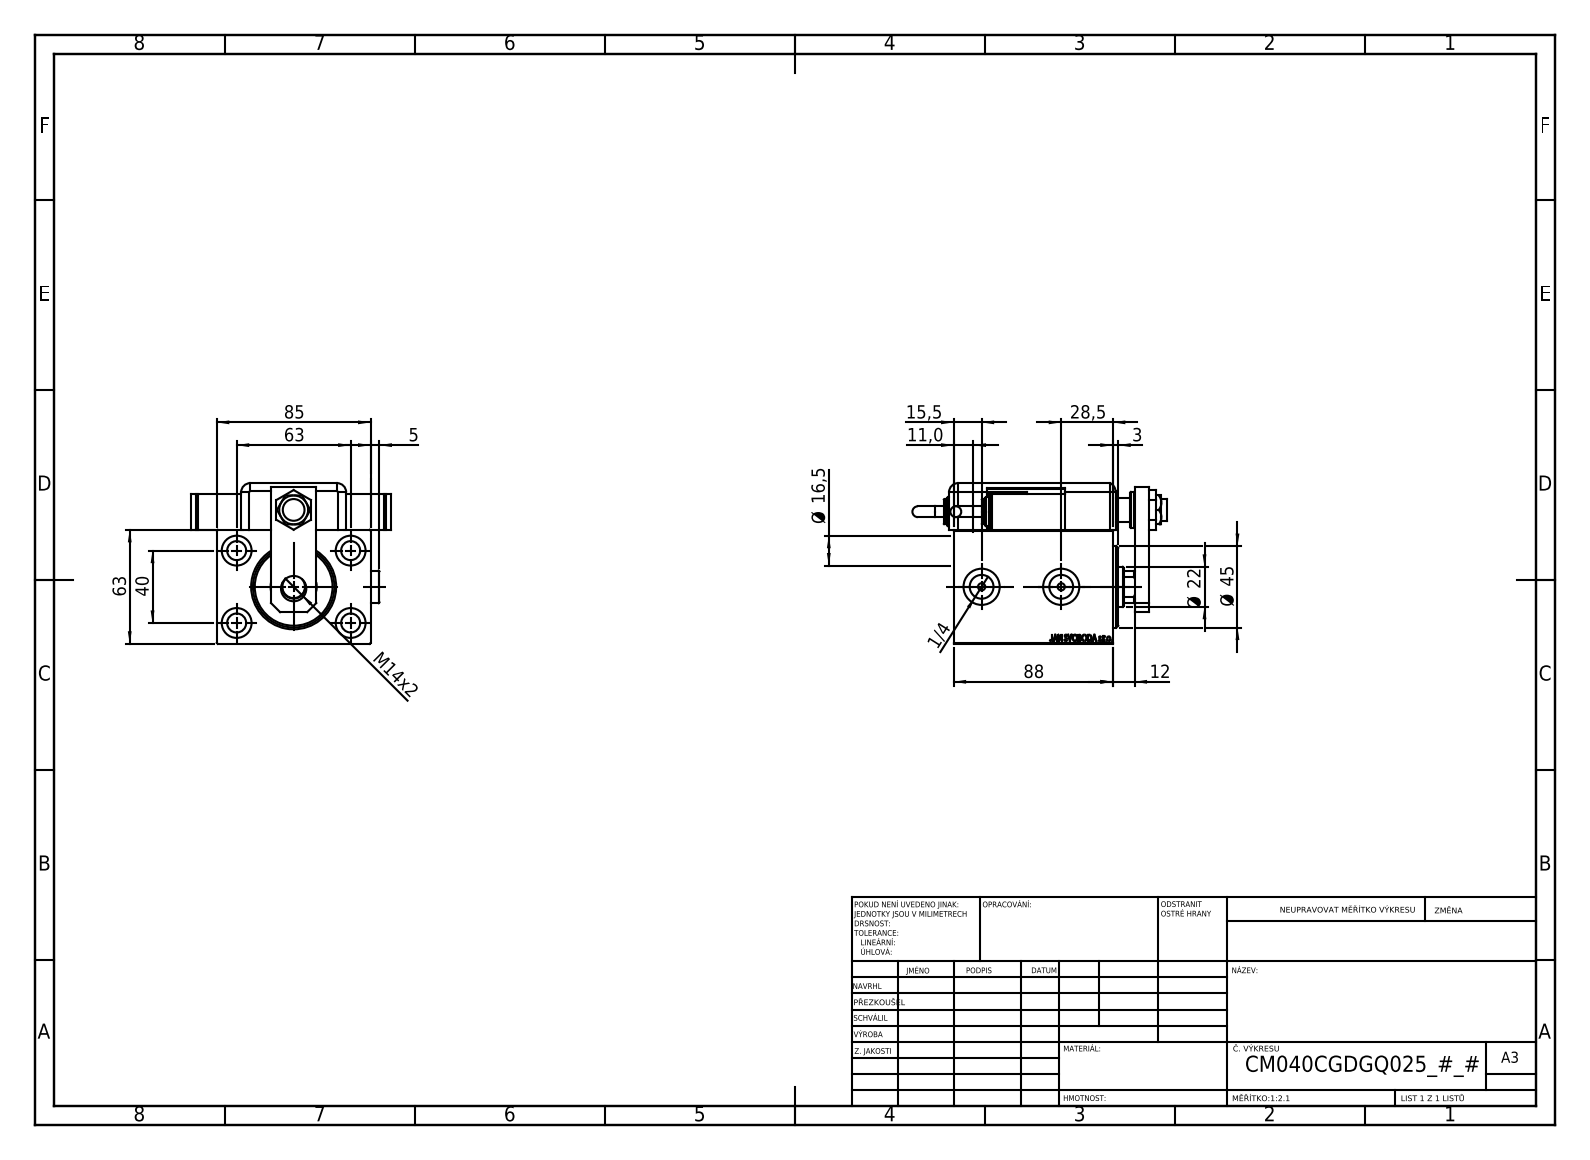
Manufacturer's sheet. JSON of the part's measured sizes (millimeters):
{"part_name": "TYC; V450CM_VC_B; KRYT; NUT_D19 (+7 more)", "step_written_by": "SolidWorks 2019 (CONFIG_CONTROL_DESIGN)", "units": "millimeters", "bodies": {"solids": 15, "faces": 1300, "planar": 648, "cylindrical": 131, "other": 521}, "overall_size": [140.46, 111, 88.8], "volume_mm3": 540819, "surface_area_mm2": 130727, "round_holes": [[4, 4], [10.5, 4], [16.5, 4], [8, 2], [13.16, 2], [14, 2], [20, 2], [12, 1], [12.5, 1], [13, 1], [22, 1], [25.5, 1]], "round_bosses_or_shafts": [[20, 3], [18, 2], [16, 2], [14, 2], [6, 2]], "partial_cylinders_radius": [[5, 9], [10, 1], [10.5, 1]], "face_to_face_distances": [3, 63, 13.5, 85, 12, 83, 10.5, 20, 88, 1.5], "hole_center_spacings": [37.31, 36.79, 37.86, 38.71, 40, 63, 69.99, 74.63]}
